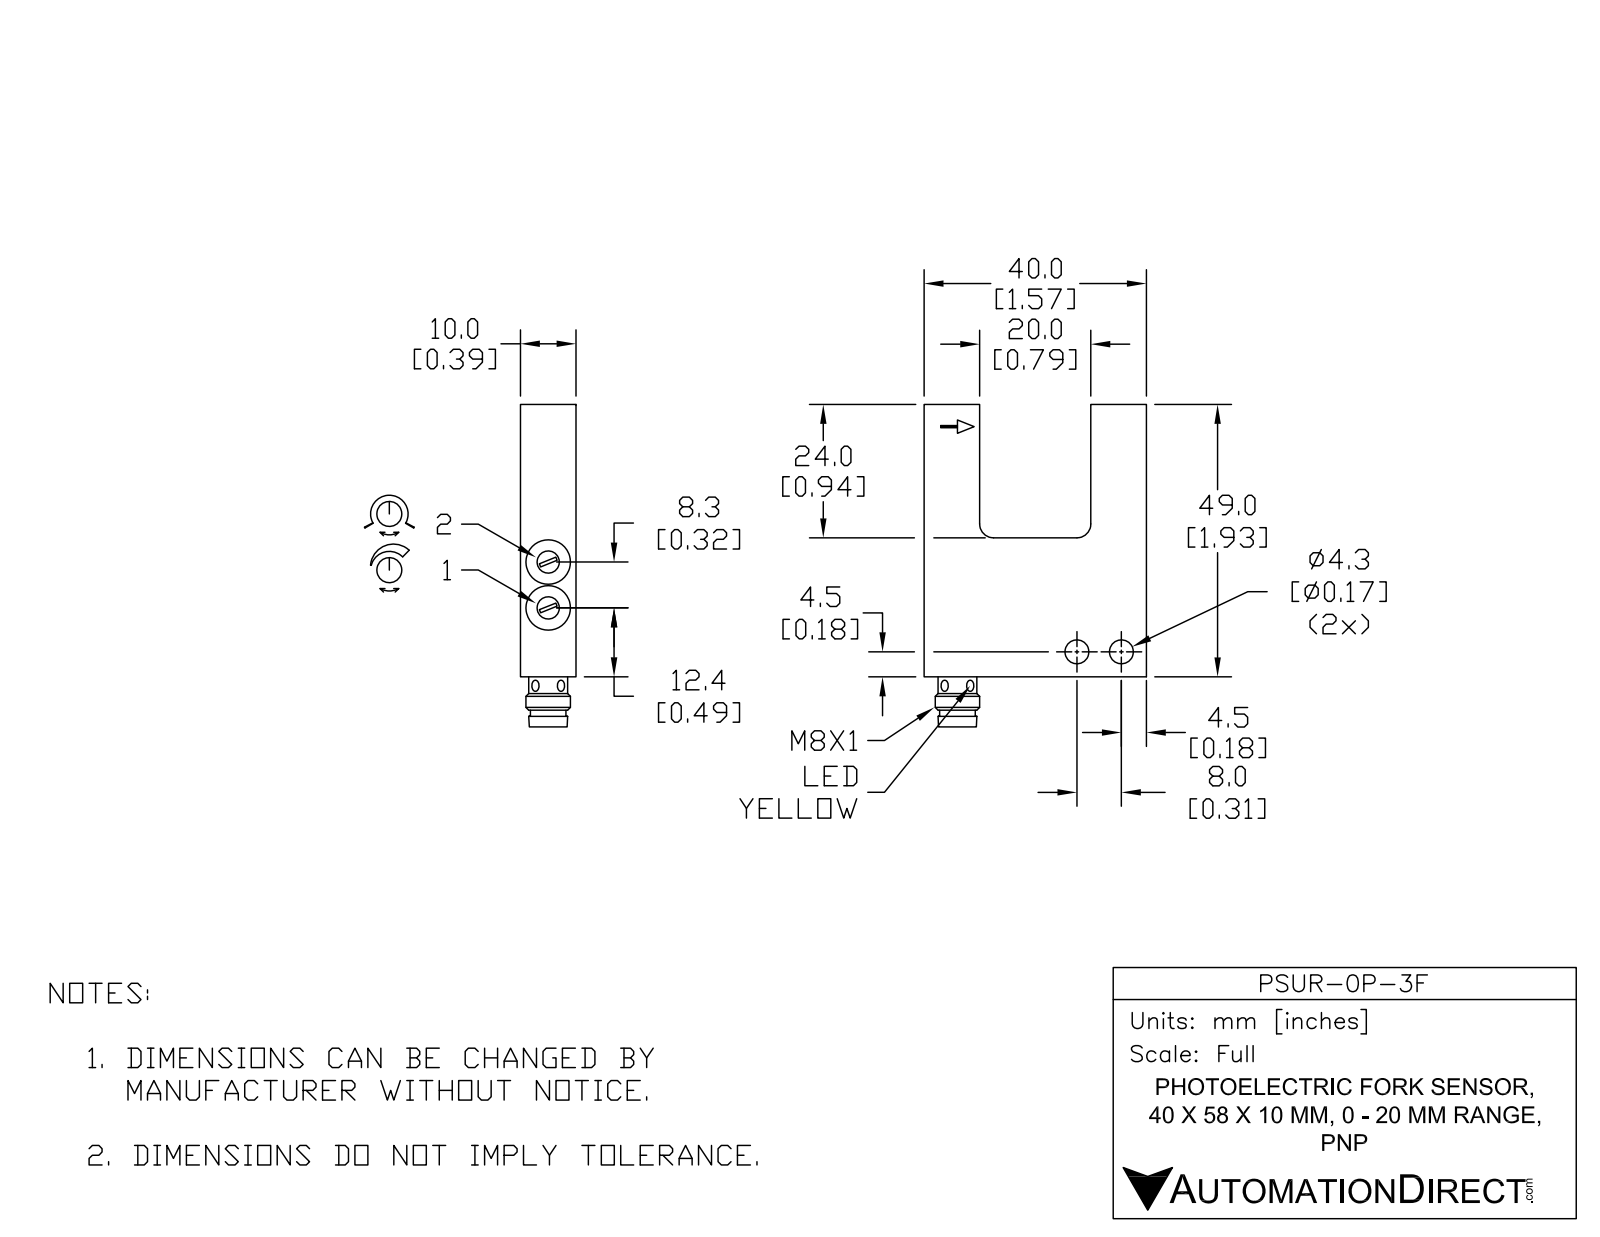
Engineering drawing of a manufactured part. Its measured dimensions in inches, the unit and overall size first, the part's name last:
Units: inches
Overall size (bounding box): 2.283 × 1.575 × 0.394
Round holes (diameter × count): ⌀0.079 ×2, ⌀0.157 ×2, ⌀0.169 ×2, ⌀0.315 ×2, ⌀0.228 ×1
Round bosses / shafts (diameter × count): ⌀0.315 ×1, ⌀0.267 ×1
Partial cylindrical surfaces — rounded edges, fillets, slot ends (radius × count): R0.02 ×8, R0.063 ×2, R0.098 ×2
Main face-to-face distances: 0.394, 1.181, 1.575, 0.787, 1.929, 0.945, 0.984, 0.39, 1.571, 1.177
Hole centre spacings: 0.315, 0.325
Volume: 0.899 in³ · Surface area: 8.869 in²
Bodies: 1 solid, 84 faces (35 planar, 43 cylindrical, 6 other)
Part name (STEP PRODUCT): PSUR-0P-3F
STEP written by: SolidWorks 2016 (AUTOMOTIVE_DESIGN)
